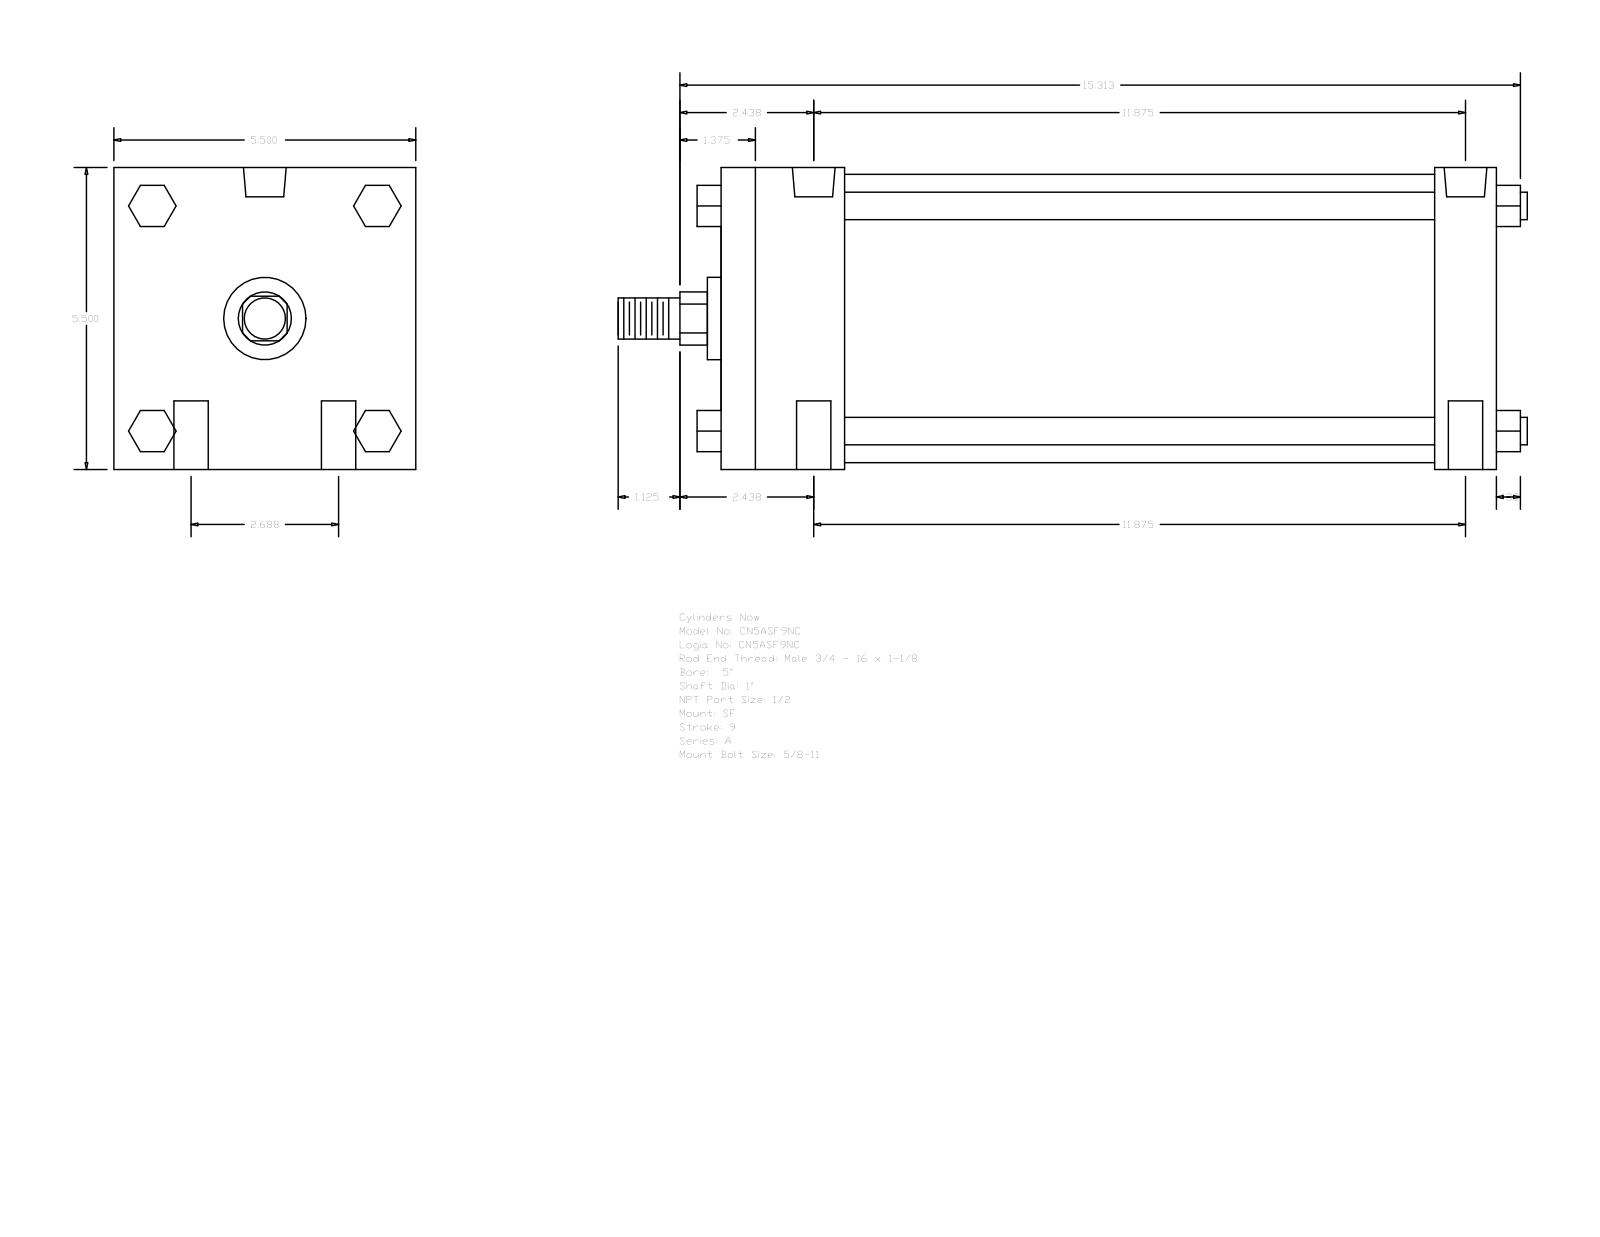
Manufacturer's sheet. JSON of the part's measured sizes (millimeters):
{"part_name": "A_SF__0500_1", "step_written_by": "GSSL Pune (CONFIG_CONTROL_DESIGN)", "units": "millimeters", "bodies": {"solids": 0, "faces": 124, "planar": 94, "cylindrical": 30, "other": 0}, "overall_size": [420.69, 139.7, 139.7], "round_holes": [[15.88, 4], [8.73, 2], [19.77, 2]], "round_bosses_or_shafts": [[12.7, 4], [133.35, 1], [38.1, 1], [25.4, 1], [19.05, 1]], "partial_cylinders_radius": [[12.29, 1]], "face_to_face_distances": [139.7, 358.77, 28.57, 57.15, 330.2, 273.05, 301.62, 19.05, 52.07, 90.18], "hole_center_spacings": [34.13, 303.55, 301.63, 68.26, 309.26, 296.85]}
